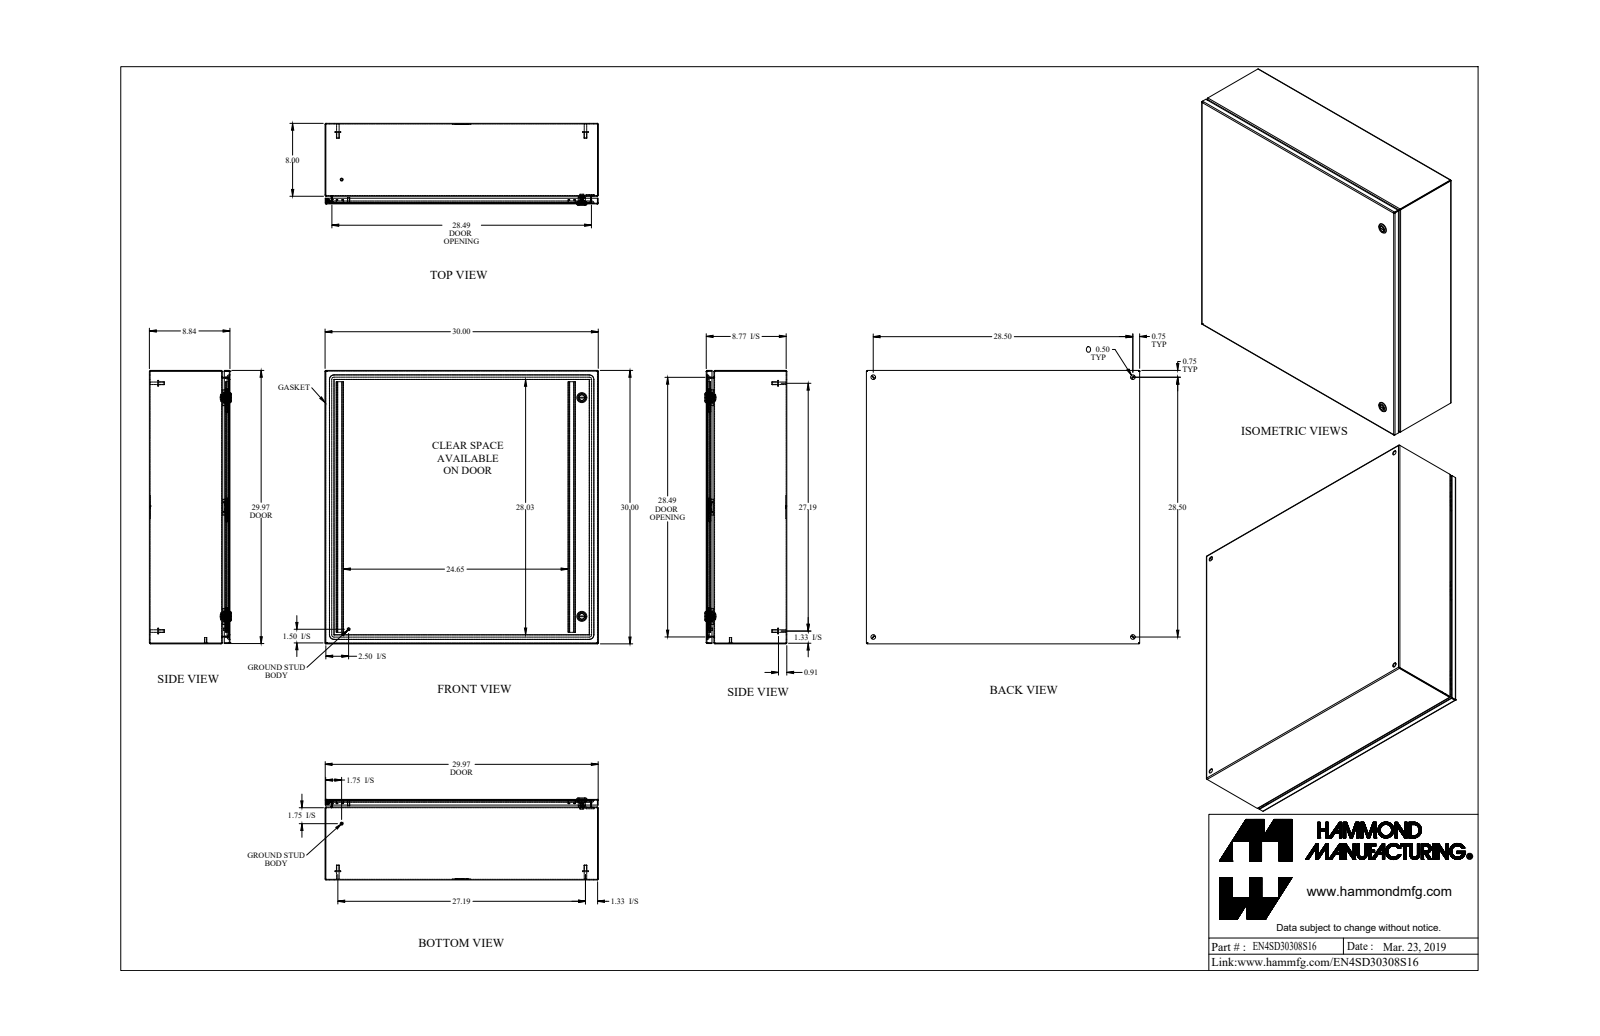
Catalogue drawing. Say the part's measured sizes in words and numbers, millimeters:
The part is named "EN4SD30308S16_Default". Its 3-D file was written by "SolidWorks 2019 (CONFIG_CONTROL_DESIGN)". It is 33 solids with 922 faces: 450 planar, 300 cylindrical and 172 other. Overall it measures 762 by 762 by 228.7 millimeters. Its volume is 3 785 000 cubic millimeters and its surface area 4 177 000 square millimeters. Round holes: 6 of diameter 12.7, 2 of diameter 5, 2 of diameter 9.8, 2 of diameter 16, 2 of diameter 19.5, 1 of diameter 4.4, 1 of diameter 6.1, 1 of diameter 6.1. Round bosses or shafts: 6 of diameter 15.9, 6 of diameter 8, 4 of diameter 7, 2 of diameter 27.9, 2 of diameter 19.9, 2 of diameter 13.3, 2 of diameter 6.4, 2 of diameter 6. Partial cylindrical surfaces (rounded edges, fillets, slot ends): 20 of radius 0.9, 20 of radius 2.7, 16 of radius 6.4, 12 of radius 0.3, 12 of radius 1.2, 6 of radius 0.2, 6 of radius 1.6, 4 of radius 3.2. The main face-to-face distances are 1.8, 222.8, 760.2, 220.9, 224.6, 758.3, 762, 21.4, 201.4, 19.1. The hole center spacings are 723.9, 1023.7, 62.8, 63.6, 609.6, 666.9, 667.7, 699.3.
